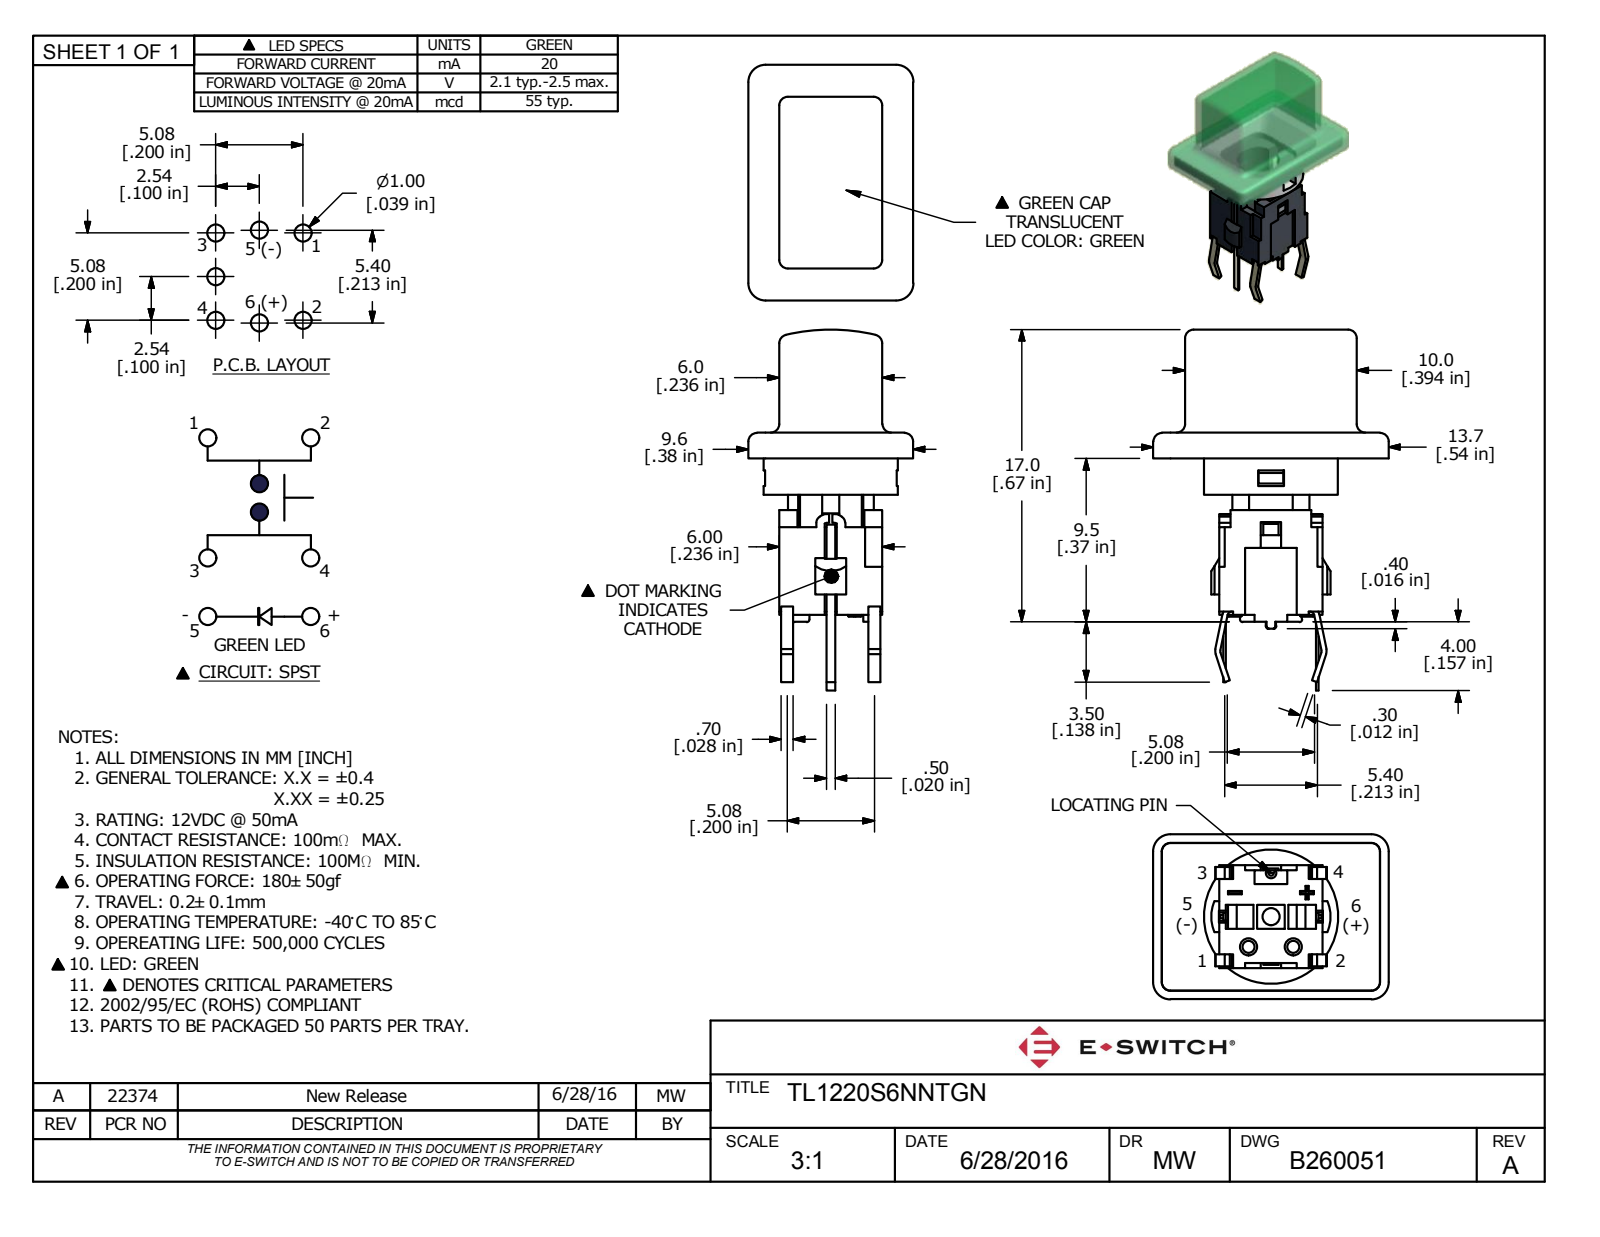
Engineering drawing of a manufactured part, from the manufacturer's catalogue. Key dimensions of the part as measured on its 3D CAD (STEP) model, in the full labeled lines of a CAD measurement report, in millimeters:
Part name (STEP PRODUCT): TL1220S6NNTGN
STEP written by: Autodesk Inventor 2022 (AUTOMOTIVE_DESIGN)
Units: millimetres
Bodies: 3 solids, 436 faces (333 planar, 77 cylindrical, 26 other)
Overall size (bounding box): 21 × 13.7 × 9.6
Volume: 440 mm³ · Surface area: 1 536 mm²
Round holes (diameter × count): ⌀1 ×1, ⌀3.7 ×1
Round bosses / shafts (diameter × count): ⌀1 ×2, ⌀7.8 ×1
Partial cylindrical surfaces — rounded edges, fillets, slot ends (radius × count): R0.5 ×14, R1 ×9, R0.3 ×4, R0.4 ×4, R0.6 ×4, R1.1 ×3, R2.3 ×2, R0.2 ×1
Main face-to-face distances: 0.5, 5.5, 6, 0.7, 1.5, 1, 7.5, 4.3, 0.8, 4.6
